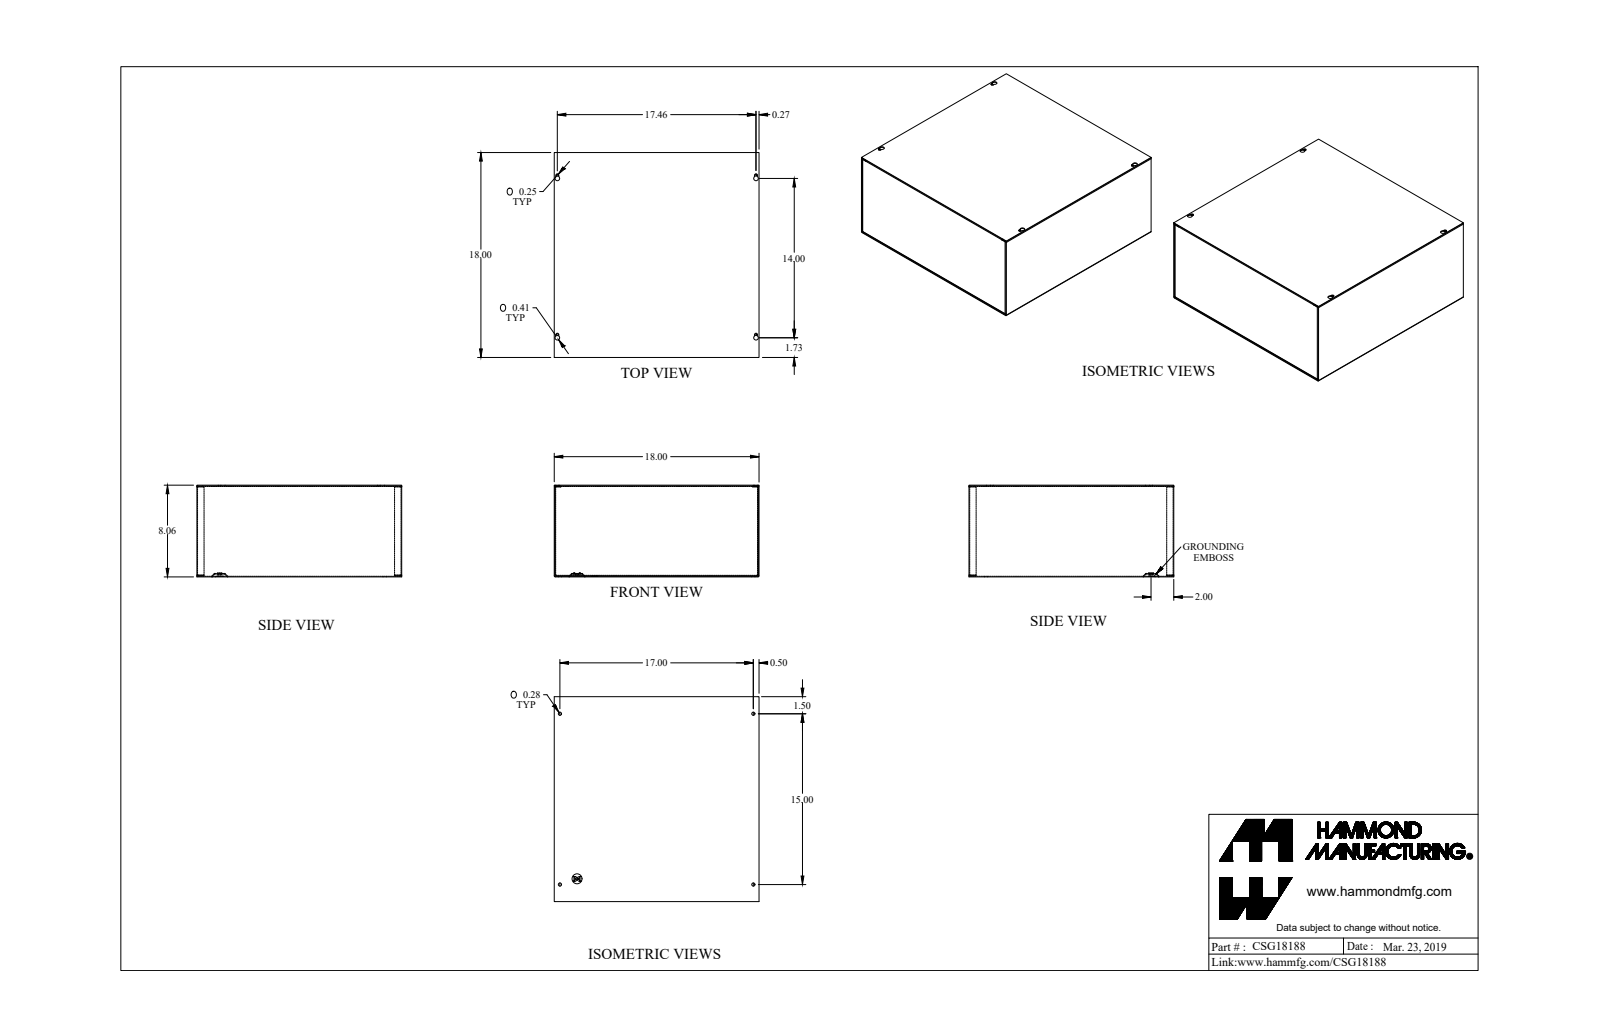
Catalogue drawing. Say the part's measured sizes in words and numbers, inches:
The part is named "CSG18188_Default". Its 3-D file was written by "SolidWorks 2019 (CONFIG_CONTROL_DESIGN)". It is 4 solids with 205 faces: 125 planar, 72 cylindrical and 8 other. Overall it measures 18 by 18 by 8.057 inches. Its volume is 72.98 cubic inches and its surface area 2 578 square inches. Round holes: 5 of diameter 0.17, 4 of diameter 0.281, 1 of diameter 0.5. Round bosses or shafts: 1 of diameter 0.492, 1 of diameter 0.284. Partial cylindrical surfaces (rounded edges, fillets, slot ends): 12 of radius 0.029, 12 of radius 0.086, 8 of radius 0.057, 4 of radius 0.125, 4 of radius 0.203. The main face-to-face distances are 0.057, 8, 17.943, 7.943, 8.057, 18, 17.886, 0.08, 7.863, 7.92. The hole center spacings are 0.55, 14.502, 17.237, 22.519, 14, 15, 17, 17.46.
